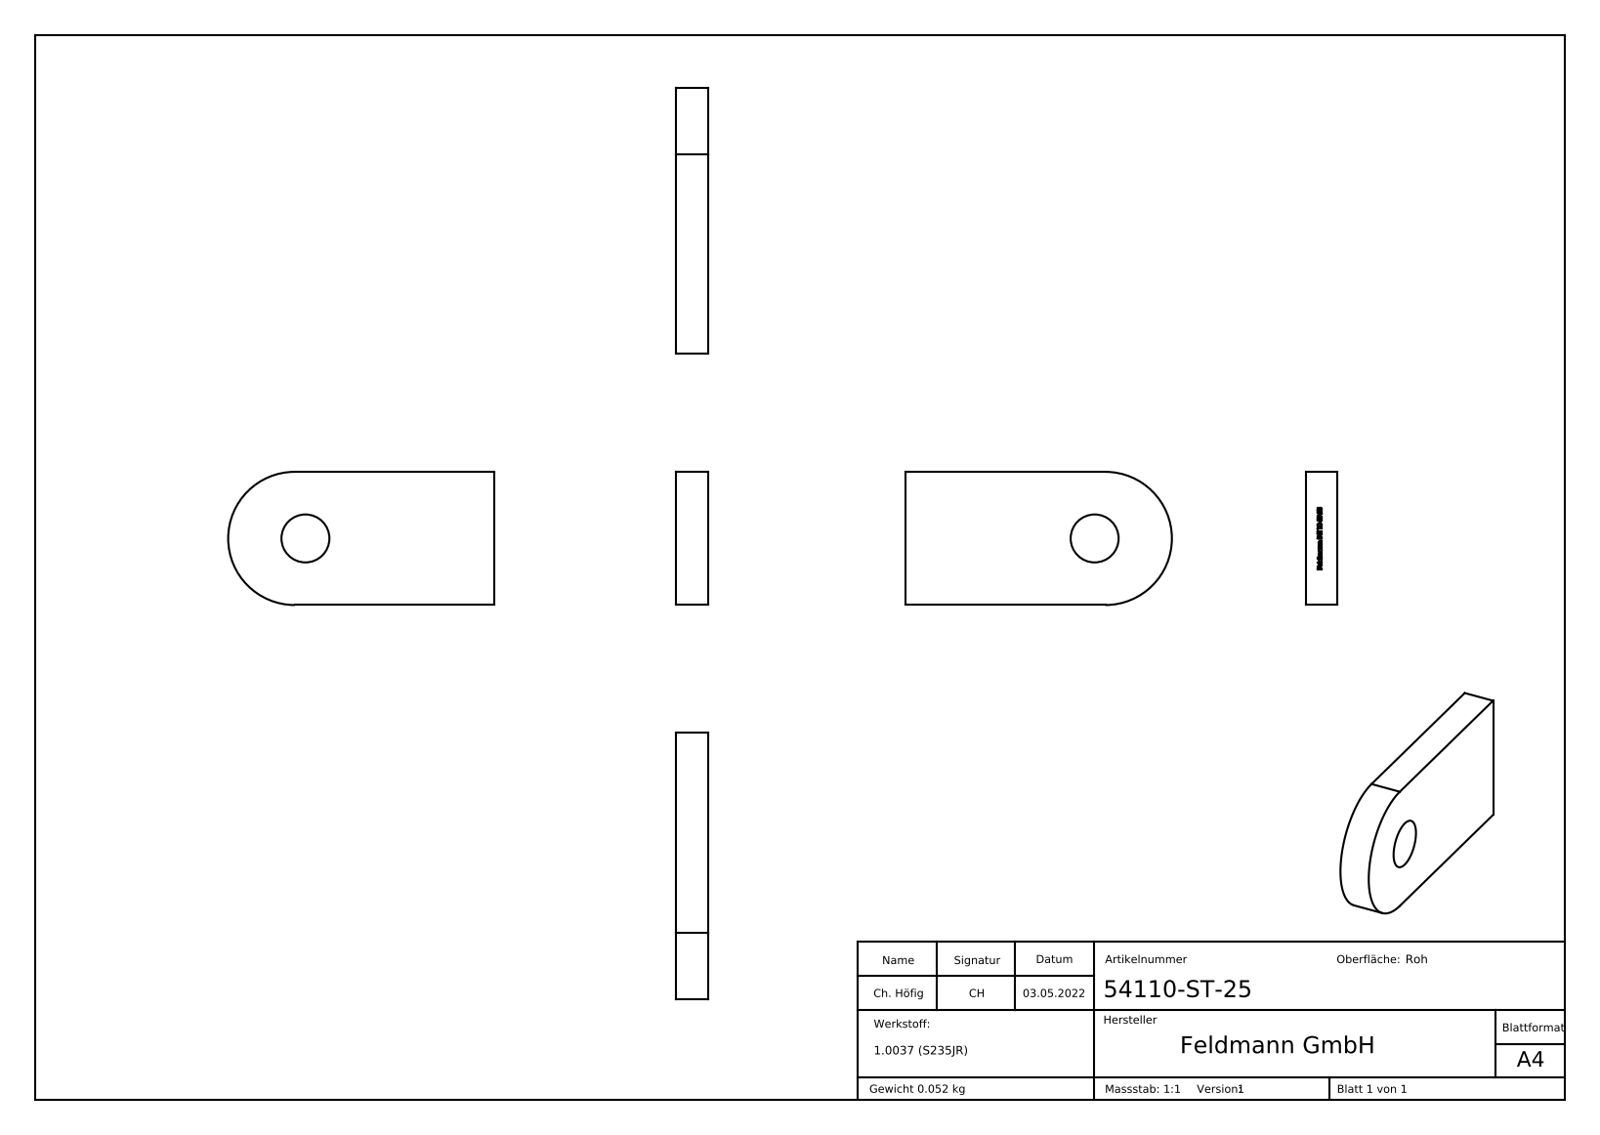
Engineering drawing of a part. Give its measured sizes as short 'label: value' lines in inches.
name: 54110-ST-25
written by: SolidWorks 2018 (CONFIG_CONTROL_DESIGN)
unit: in
bodies: 1 solid, 240 faces (144 planar, 2 cylindrical, 94 other)
size: 1.969 × 0.984 × 0.236
volume: 0.41 in³; area: 5.038 in²
holes: 1× ⌀0.354
rounds: 1× R0.492
face distances: 0.236, 0.984, 0.118, 0.104, 0.334, 0.024, 0.028, 0.149, 0.087, 0.027
